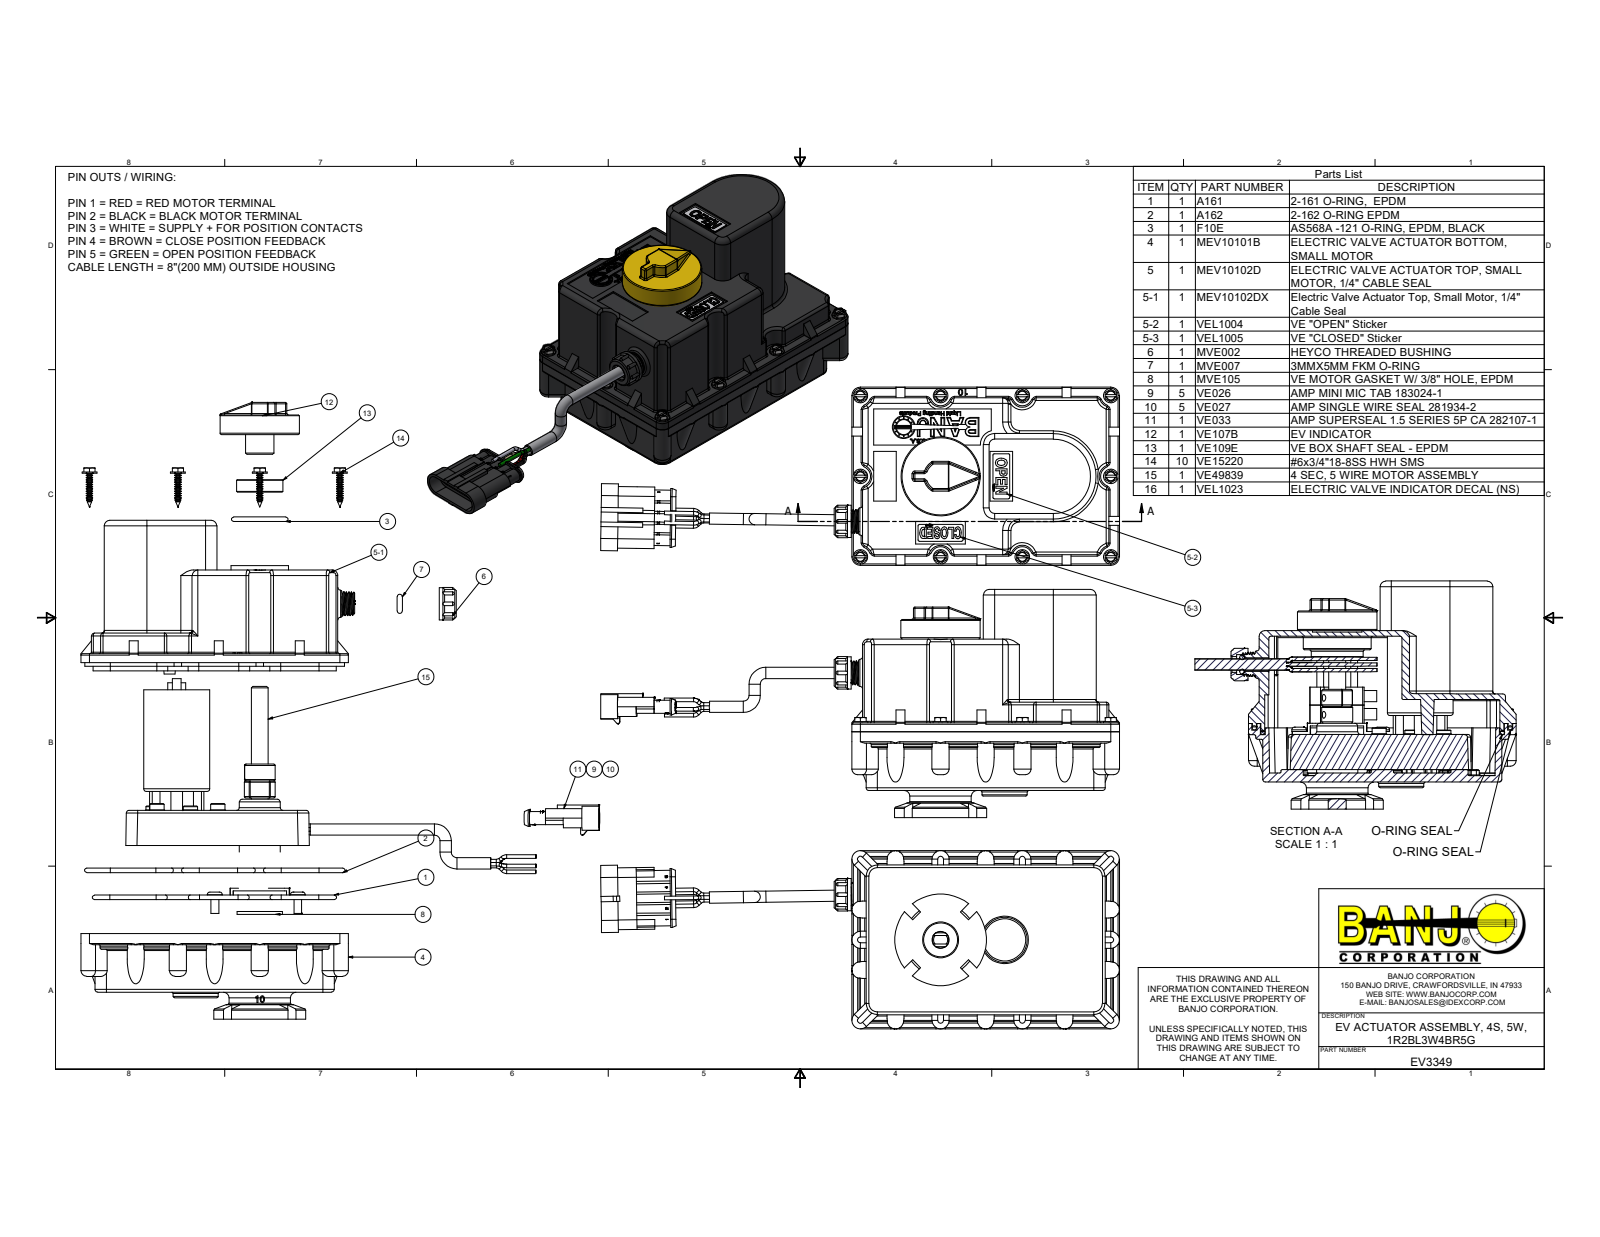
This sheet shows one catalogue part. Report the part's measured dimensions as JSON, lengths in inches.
{"part_name": "EV3349; MEV10101B; MEV10102D; MEV10102DX (+8 more)", "step_written_by": "Autodesk Inventor 2022 (AUTOMOTIVE_DESIGN)", "units": "inches", "bodies": {"solids": 48, "faces": 5033, "planar": 2232, "cylindrical": 1336, "other": 1465}, "overall_size": [11.5, 5.055, 3.95], "volume_in3": 34.92, "surface_area_in2": 398.4, "round_holes": [[0.16, 12], [0.11, 10], [0.2, 10], [0.12, 6], [0.15, 6], [0.176, 6], [0.055, 5], [0.217, 5], [0.1, 3], [0.13, 2], [0.3, 1], [0.34, 1]], "round_bosses_or_shafts": [[0.08, 19], [0.328, 10], [0.138, 10], [0.103, 8], [0.232, 5], [0.173, 5], [0.154, 5], [0.134, 5]], "partial_cylinders_radius": [[0.03, 121], [0.02, 63], [0.06, 47], [0.125, 24], [0.315, 24], [0.5, 24], [0.02, 21], [0.007, 20]], "face_to_face_distances": [0.125, 3.355, 0.2, 1.1, 1.025, 3.23, 1.3, 0.075, 0.78, 0.79], "hole_center_spacings": [1.68, 2.058, 1.684, 1.785, 2.376, 0.236, 0.492, 1.188]}
